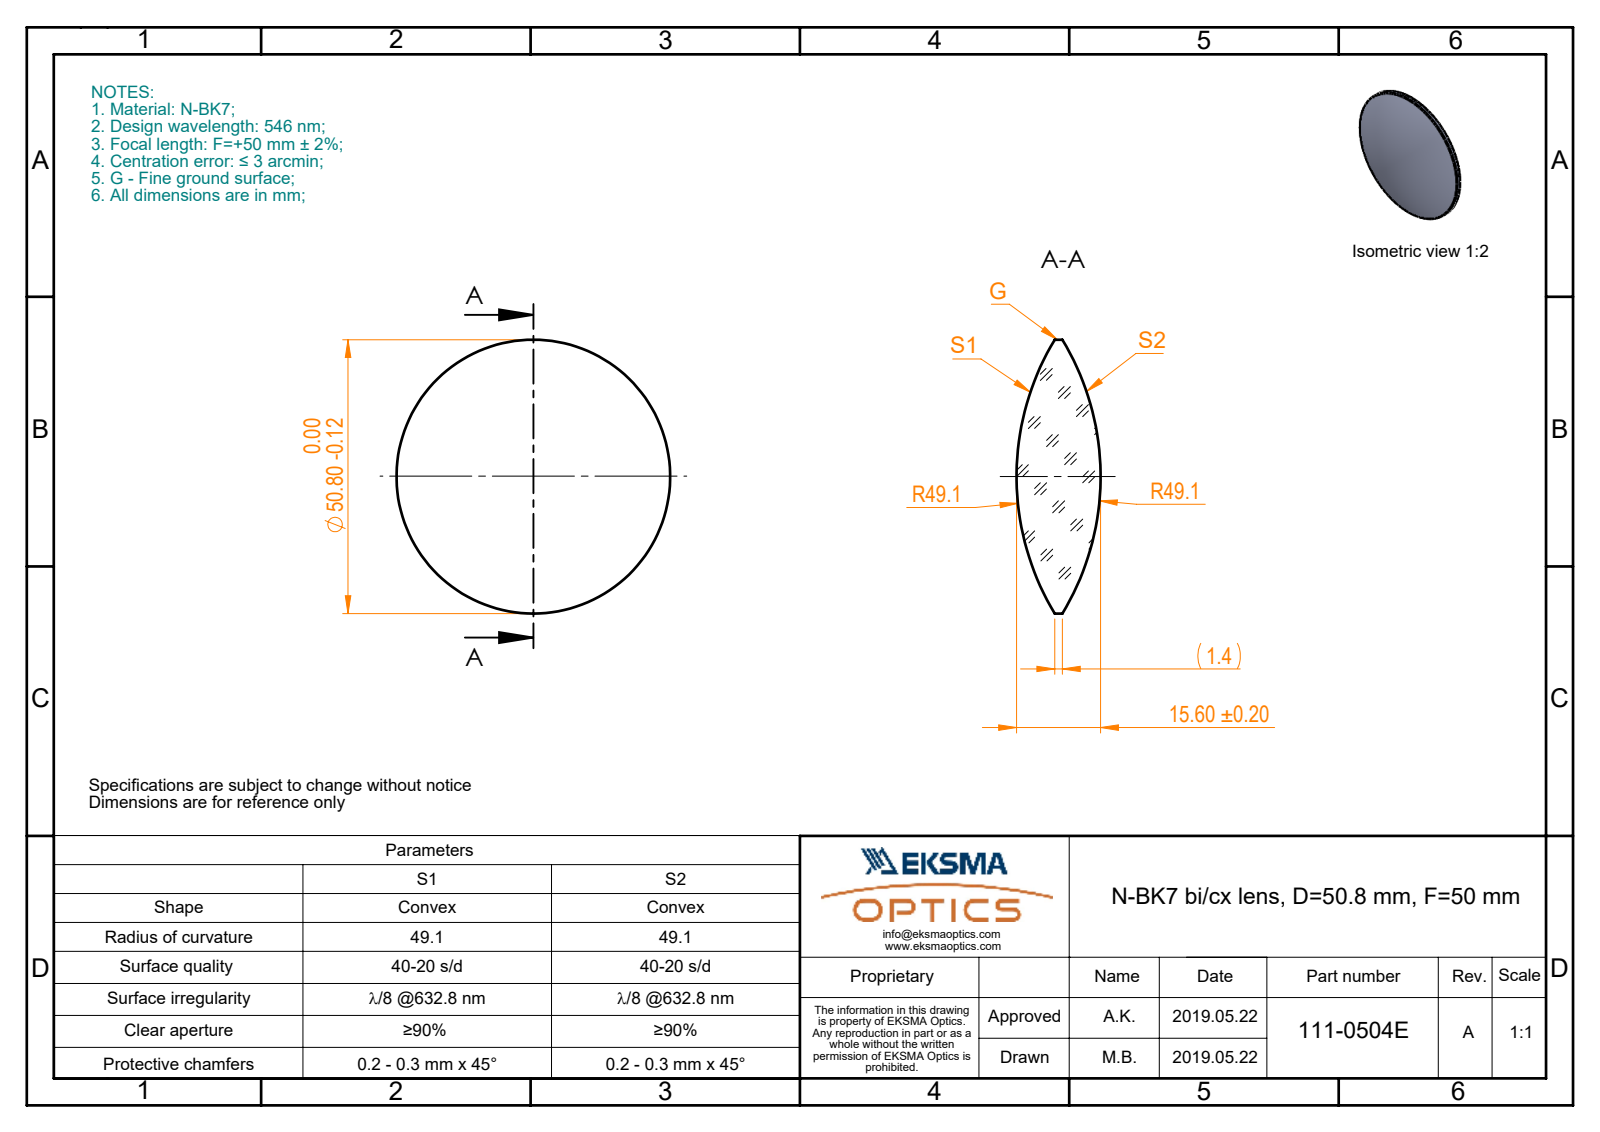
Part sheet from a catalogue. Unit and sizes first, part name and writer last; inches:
Units: inches
Overall size (bounding box): 2 × 2 × 0.614
Round bosses / shafts (diameter × count): ⌀2 ×1
Volume: 1.076 in³ · Surface area: 7.125 in²
Bodies: 1 solid, 6 faces (0 planar, 2 cylindrical, 4 other)
Part name (STEP PRODUCT): 111-0504E BK7 bi-cx 50.8 F50
STEP written by: SolidWorks 2017 (CONFIG_CONTROL_DESIGN)
